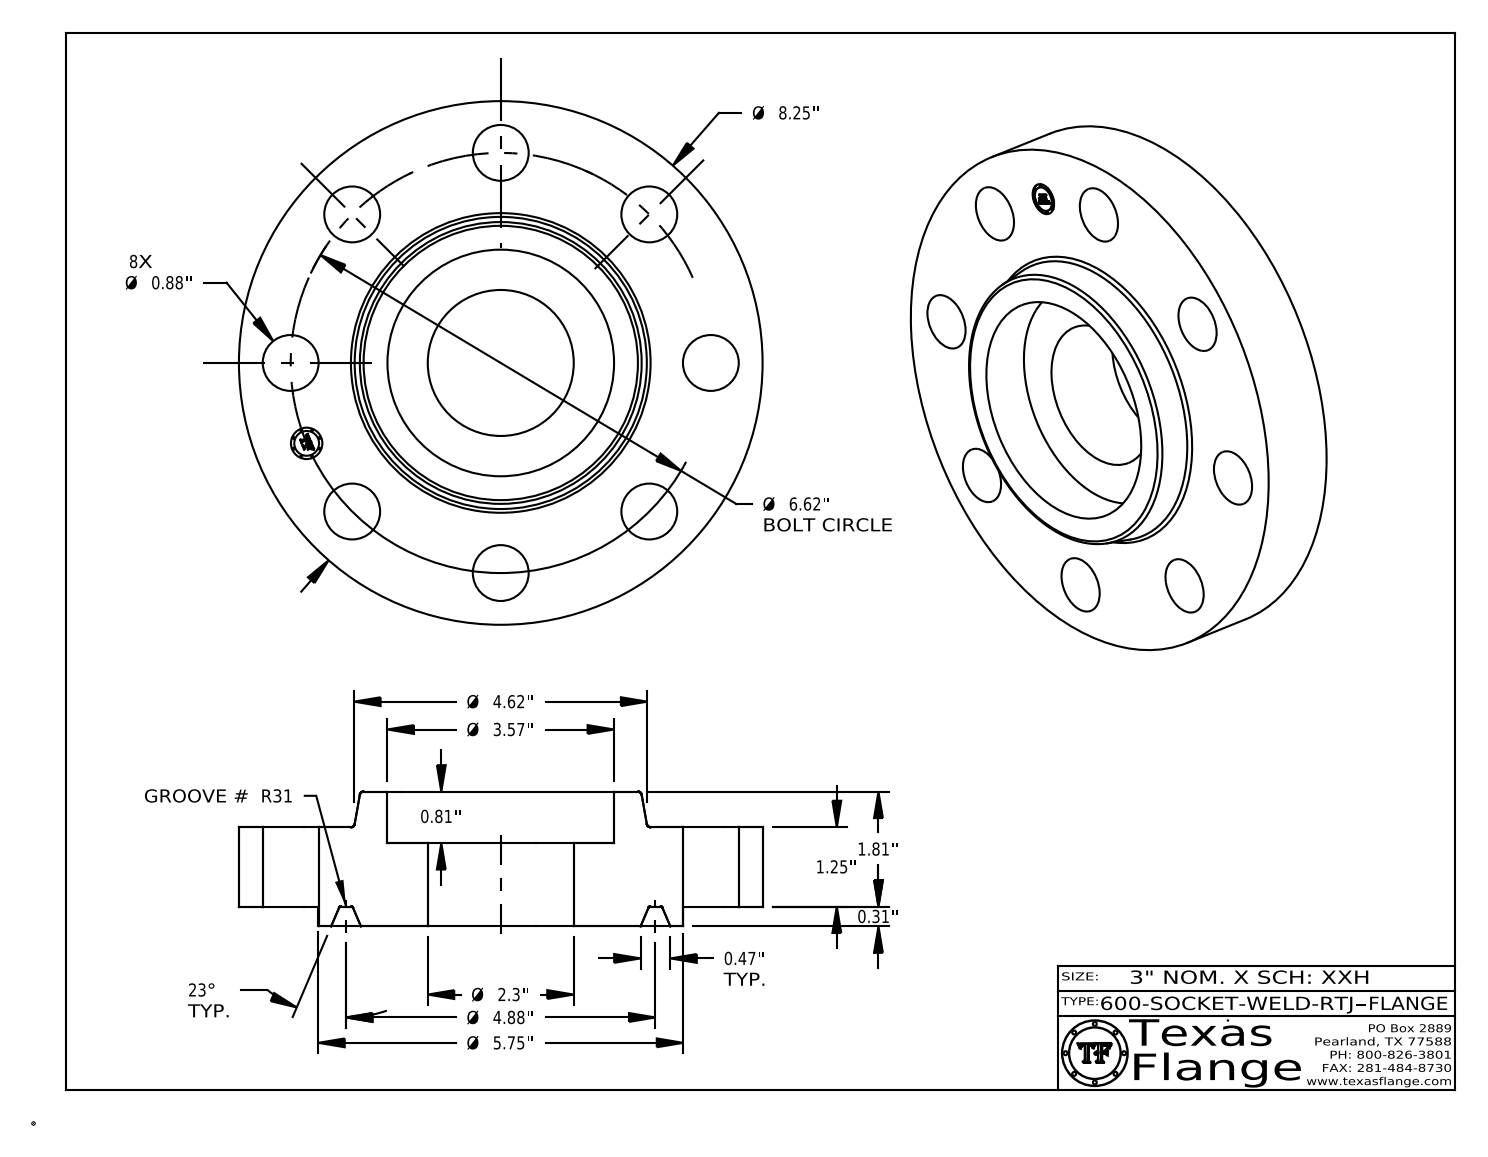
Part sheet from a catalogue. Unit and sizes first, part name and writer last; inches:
Units: inches
Overall size (bounding box): 8.25 × 8.25 × 2.123
Round holes (diameter × count): ⌀0.88 ×8, ⌀0.495 ×1, ⌀2.3 ×1, ⌀3.57 ×1
Round bosses / shafts (diameter × count): ⌀0.03 ×8, ⌀8.25 ×1, ⌀5.75 ×1, ⌀0.39 ×1
Main face-to-face distances: 1.25, 0.313, 1.563, 1.313, 1, 0.25, 2.123, 1.81, 0.81, 0.56
Hole centre spacings: 3.31, 2.533, 6.116, 4.681, 4.681, 1.291, 3.678, 6.493
Volume: 62.68 in³ · Surface area: 185.6 in²
Bodies: 1 solid, 438 faces (372 planar, 52 cylindrical, 14 other)
Part name (STEP PRODUCT): 600-SOCKET-WELD-RTJ
STEP written by: CATIA V5 STEP AP214 (AUTOMOTIVE_DESIGN)
